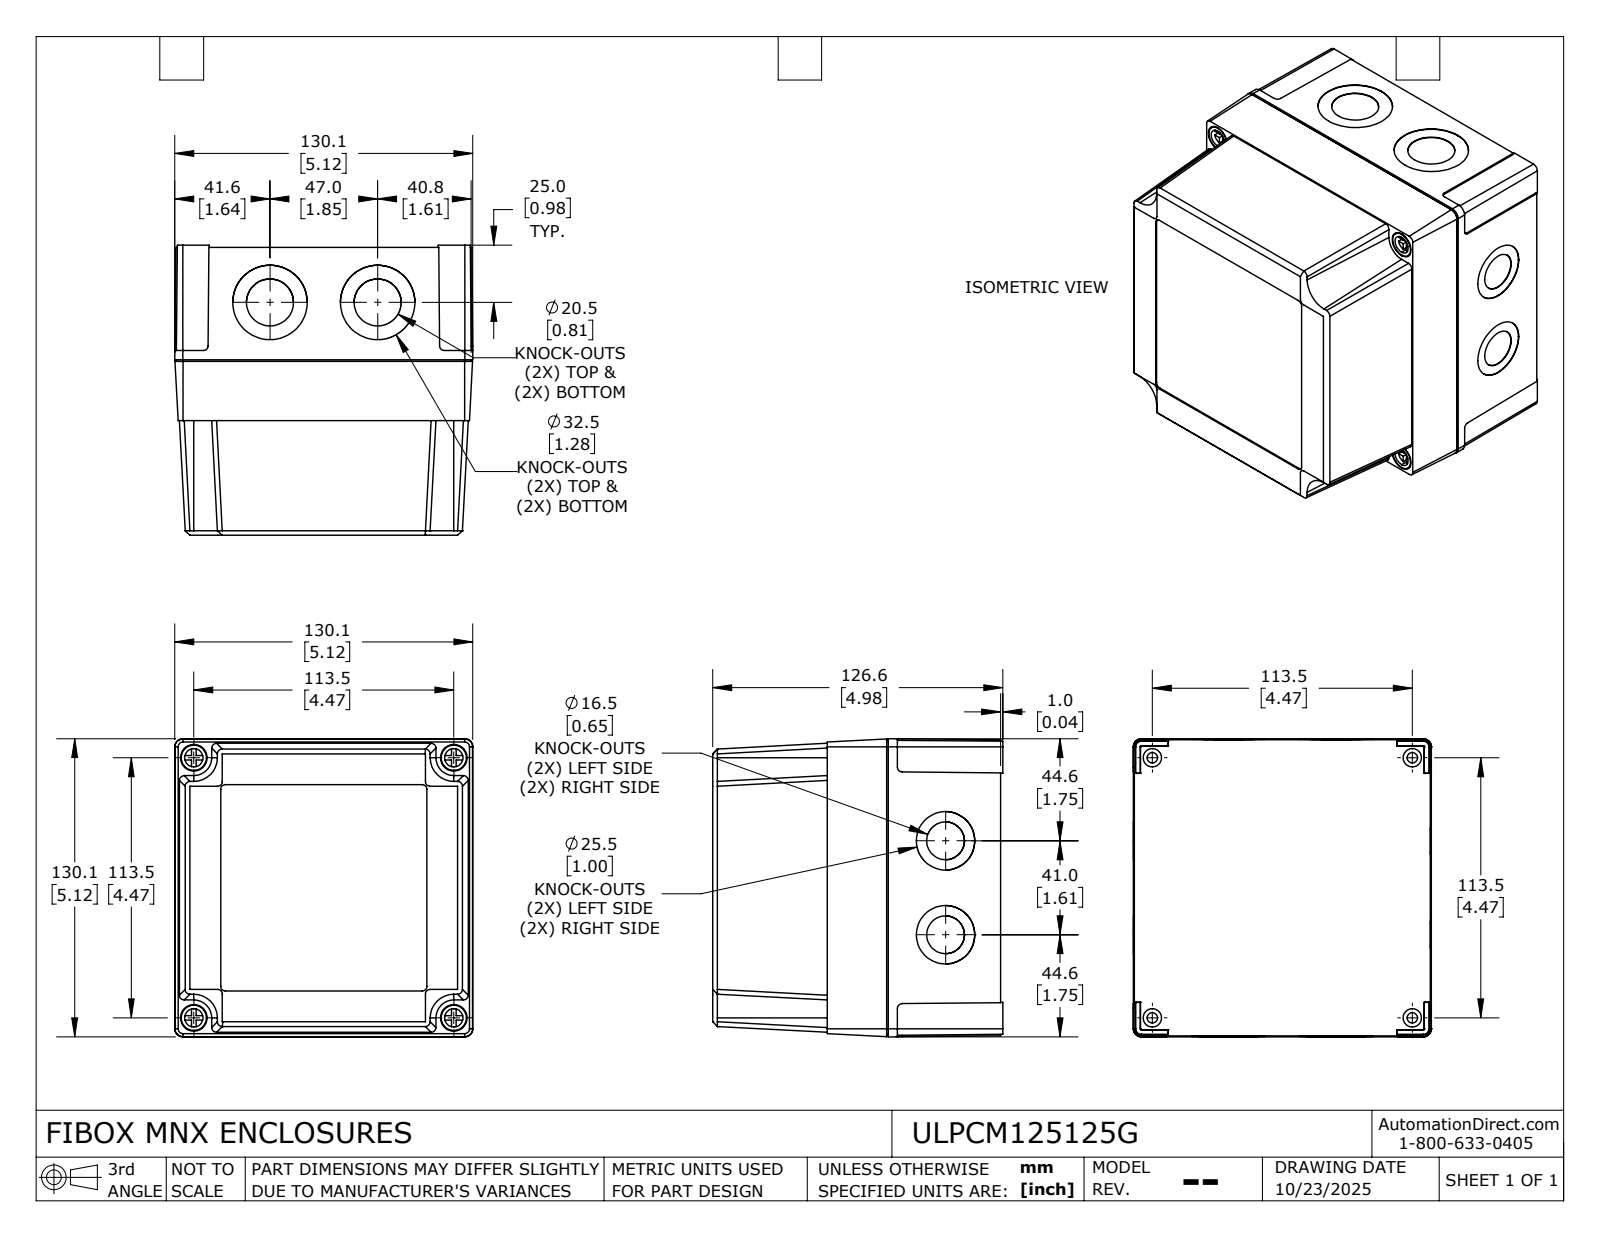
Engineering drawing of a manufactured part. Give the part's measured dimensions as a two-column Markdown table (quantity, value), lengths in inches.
| quantity | value |
| --- | --- |
| part name | ULPCM125125G_Default |
| STEP written by | SolidWorks 2024 (CONFIG_CONTROL_DESIGN) |
| units | inches |
| bodies | 6 solids, 577 faces (335 planar, 192 cylindrical, 50 other) |
| overall size | 5.122 × 5.122 × 4.984 |
| volume | 17.1 in³ |
| surface area | 308.2 in² |
| round holes (diameter × count) | 0.126 × 8, 0.157 × 8, 0.177 × 4, 0.315 × 4, 0.457 × 4, 0.65 × 4, 0.807 × 4, 1.004 × 4, 1.28 × 4 |
| round bosses / shafts (diameter × count) | 0.315 × 8, 0.098 × 8, 0.433 × 4, 0.283 × 4 |
| partial cylindrical surfaces (radius × count) | 0.079 × 8, 0.083 × 8, 0.056 × 6, 0.021 × 4, 0.197 × 4, 0.023 × 2 |
| main face-to-face distances | 0.055, 0.165, 0.118, 4.854, 4.736, 0.078, 0.022, 4.925, 4.807, 0.071 |
| hole center spacings | 2.281, 4.587, 0.888, 1.476, 1.796, 2.506, 3.543, 3.7 |
